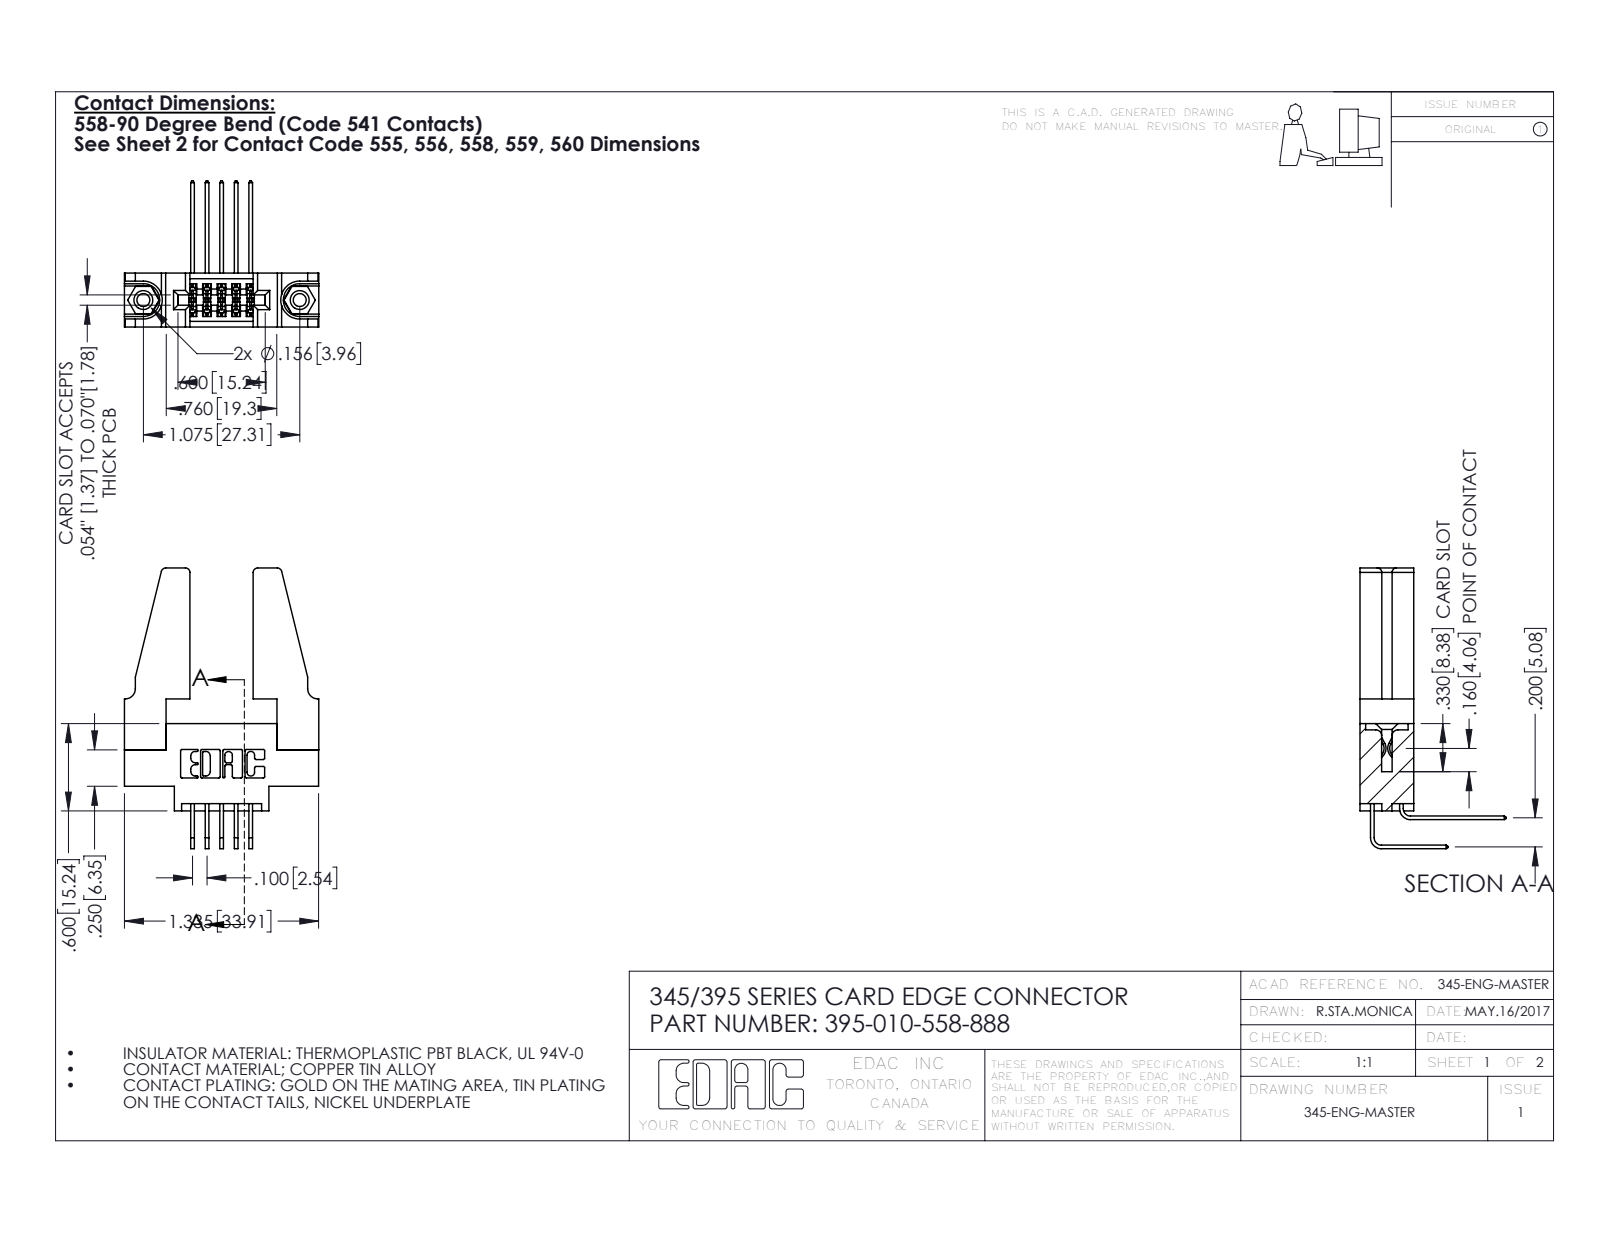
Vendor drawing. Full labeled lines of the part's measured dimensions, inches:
Part name (STEP PRODUCT): 345-292-001_558 559 Tail - 1; 345-250-001_345-250-001-102; 345 Part_0.170 Offset - 0.156 Dia-TH; 345-220-078_345-220-088 (+2 more)
STEP written by: SolidWorks 2016 (CONFIG_CONTROL_DESIGN)
Units: inches
Bodies: 15 solids, 774 faces (506 planar, 252 cylindrical, 16 other)
Overall size (bounding box): 1.929 × 1.336 × 1.005
Volume: 0.375 in³ · Surface area: 11.01 in²
Round holes (diameter × count): ⌀0.089 ×2, ⌀0.125 ×2, ⌀0.156 ×2, ⌀0.064 ×1
Round bosses / shafts (diameter × count): ⌀0.155 ×2
Partial cylindrical surfaces — rounded edges, fillets, slot ends (radius × count): R0.01 ×22, R0.006 ×16, R0.03 ×8, R0.007 ×6, R0.031 ×6, R0.026 ×3, R0.014 ×2, R0.019 ×2
Main face-to-face distances: 0.37, 0.072, 0.298, 0.2, 0.148, 0.15, 0.22, 0.077, 0.098, 0.272
Hole centre spacings: 0.27, 0.847, 1.075
